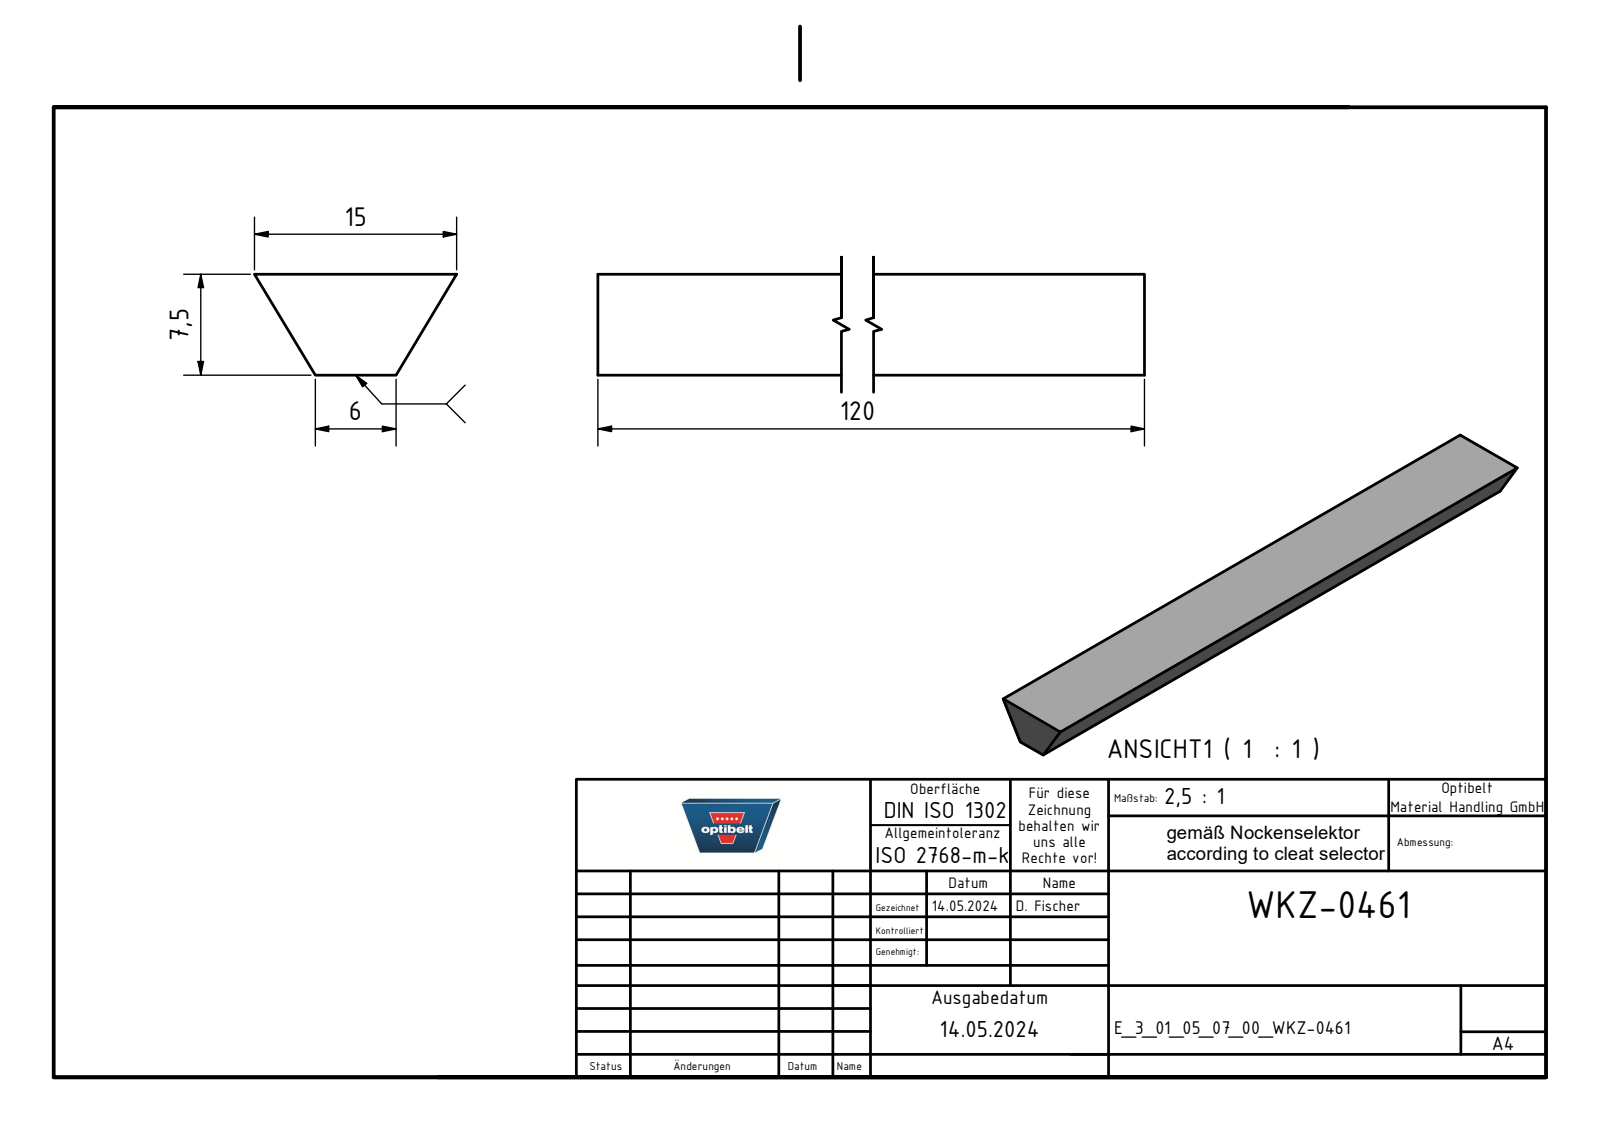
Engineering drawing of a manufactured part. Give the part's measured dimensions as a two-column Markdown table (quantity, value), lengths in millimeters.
| quantity | value |
| --- | --- |
| part name | E_3_01_05_07_00_WKZ-0461 |
| STEP written by | Autodesk Inventor 2021 (AUTOMOTIVE_DESIGN) |
| units | millimeters |
| bodies | 1 solid, 6 faces (6 planar, 0 cylindrical, 0 other) |
| overall size | 120 × 15 × 7.5 |
| volume | 9 450 mm³ |
| surface area | 4 777 mm² |
| main face-to-face distances | 7.5, 120 |
